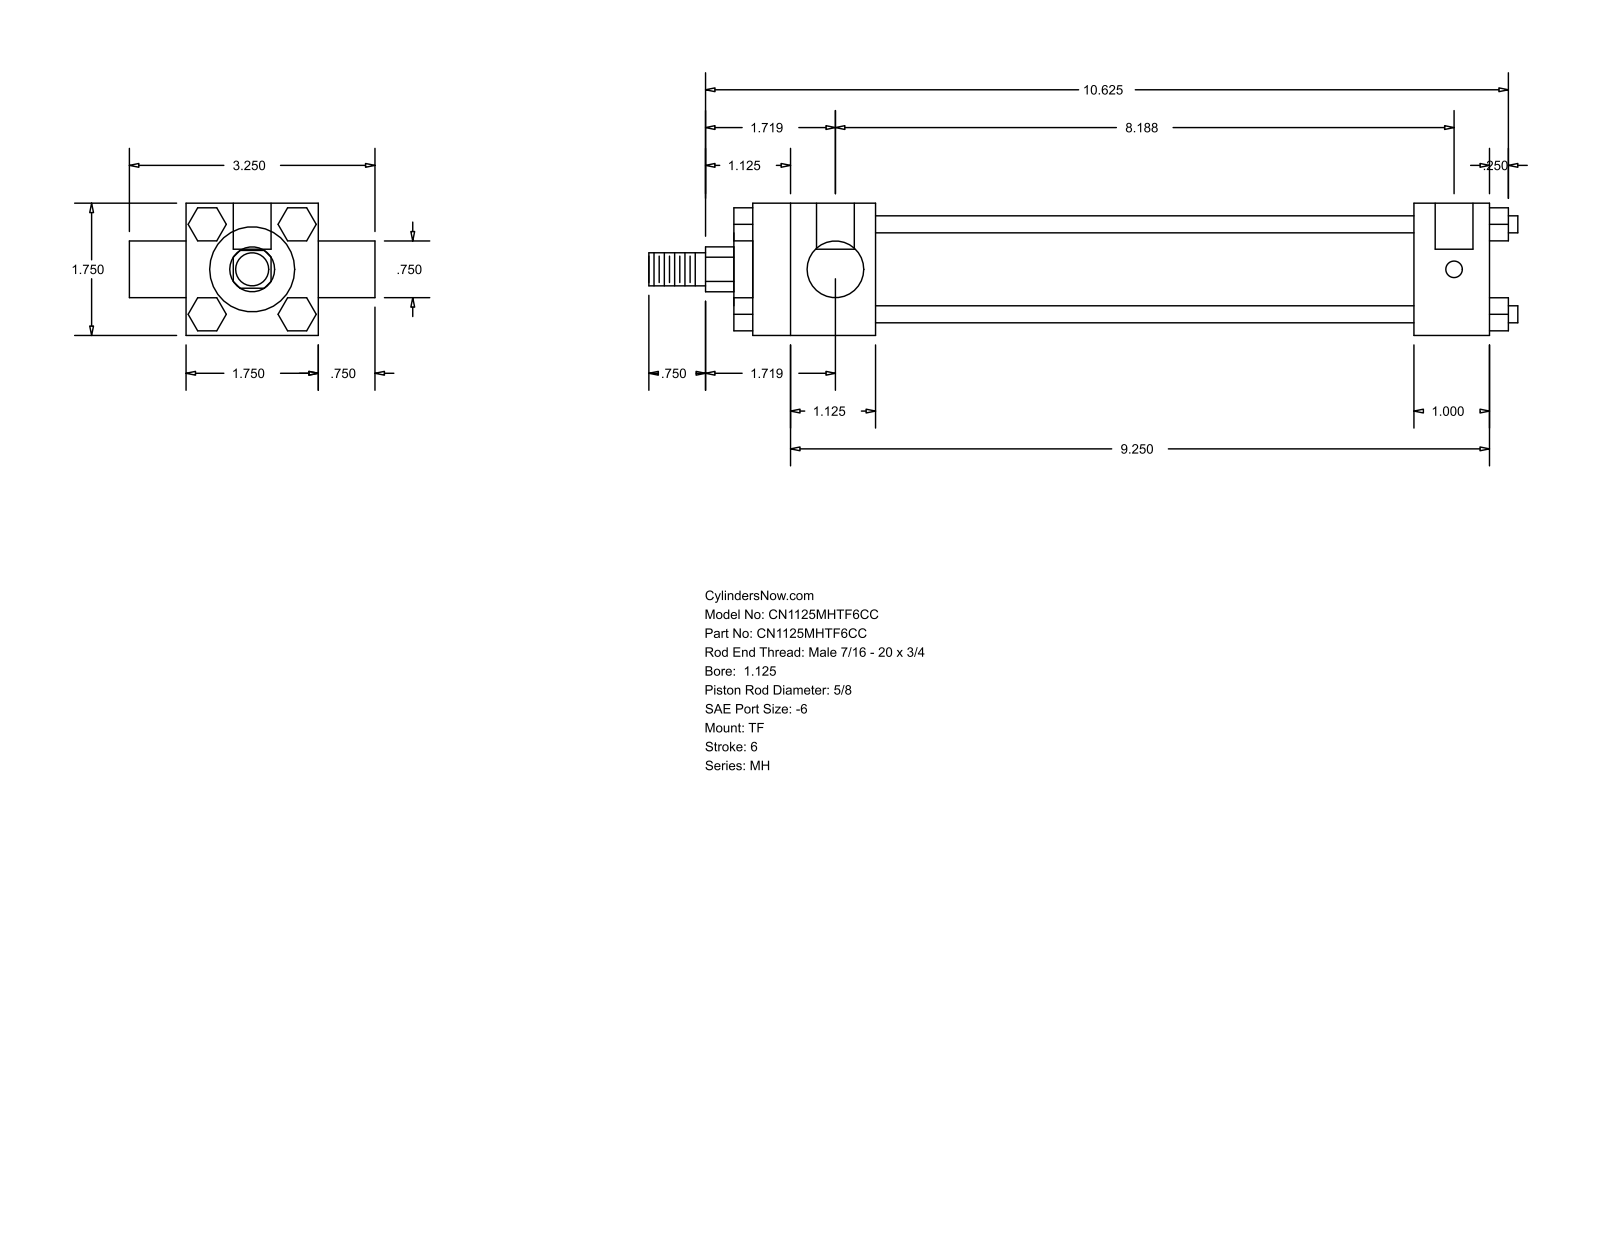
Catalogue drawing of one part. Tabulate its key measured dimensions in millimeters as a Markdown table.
| quantity | value |
| --- | --- |
| part name | MH_TF__0112_0.625 |
| STEP written by | GSSL Pune (CONFIG_CONTROL_DESIGN) |
| units | millimeters |
| bodies | 0 solids, 120 faces (92 planar, 28 cylindrical, 0 other) |
| overall size | 292.1 × 82.55 × 44.45 |
| round holes (diameter × count) | 5.56 × 3, 12.7 × 2 |
| round bosses / shafts (diameter × count) | 5.71 × 4, 34.92 × 1, 28.57 × 1, 19.05 × 1, 15.88 × 1, 11.11 × 1 |
| partial cylindrical surfaces (radius × count) | 7.54 × 1 |
| main face-to-face distances | 44.46, 11.11, 25.4, 180.97, 206.37, 41.27, 222.24, 247.64, 47.62, 6.35 |
| hole center spacings | 3.17, 204.79, 207.96 |
